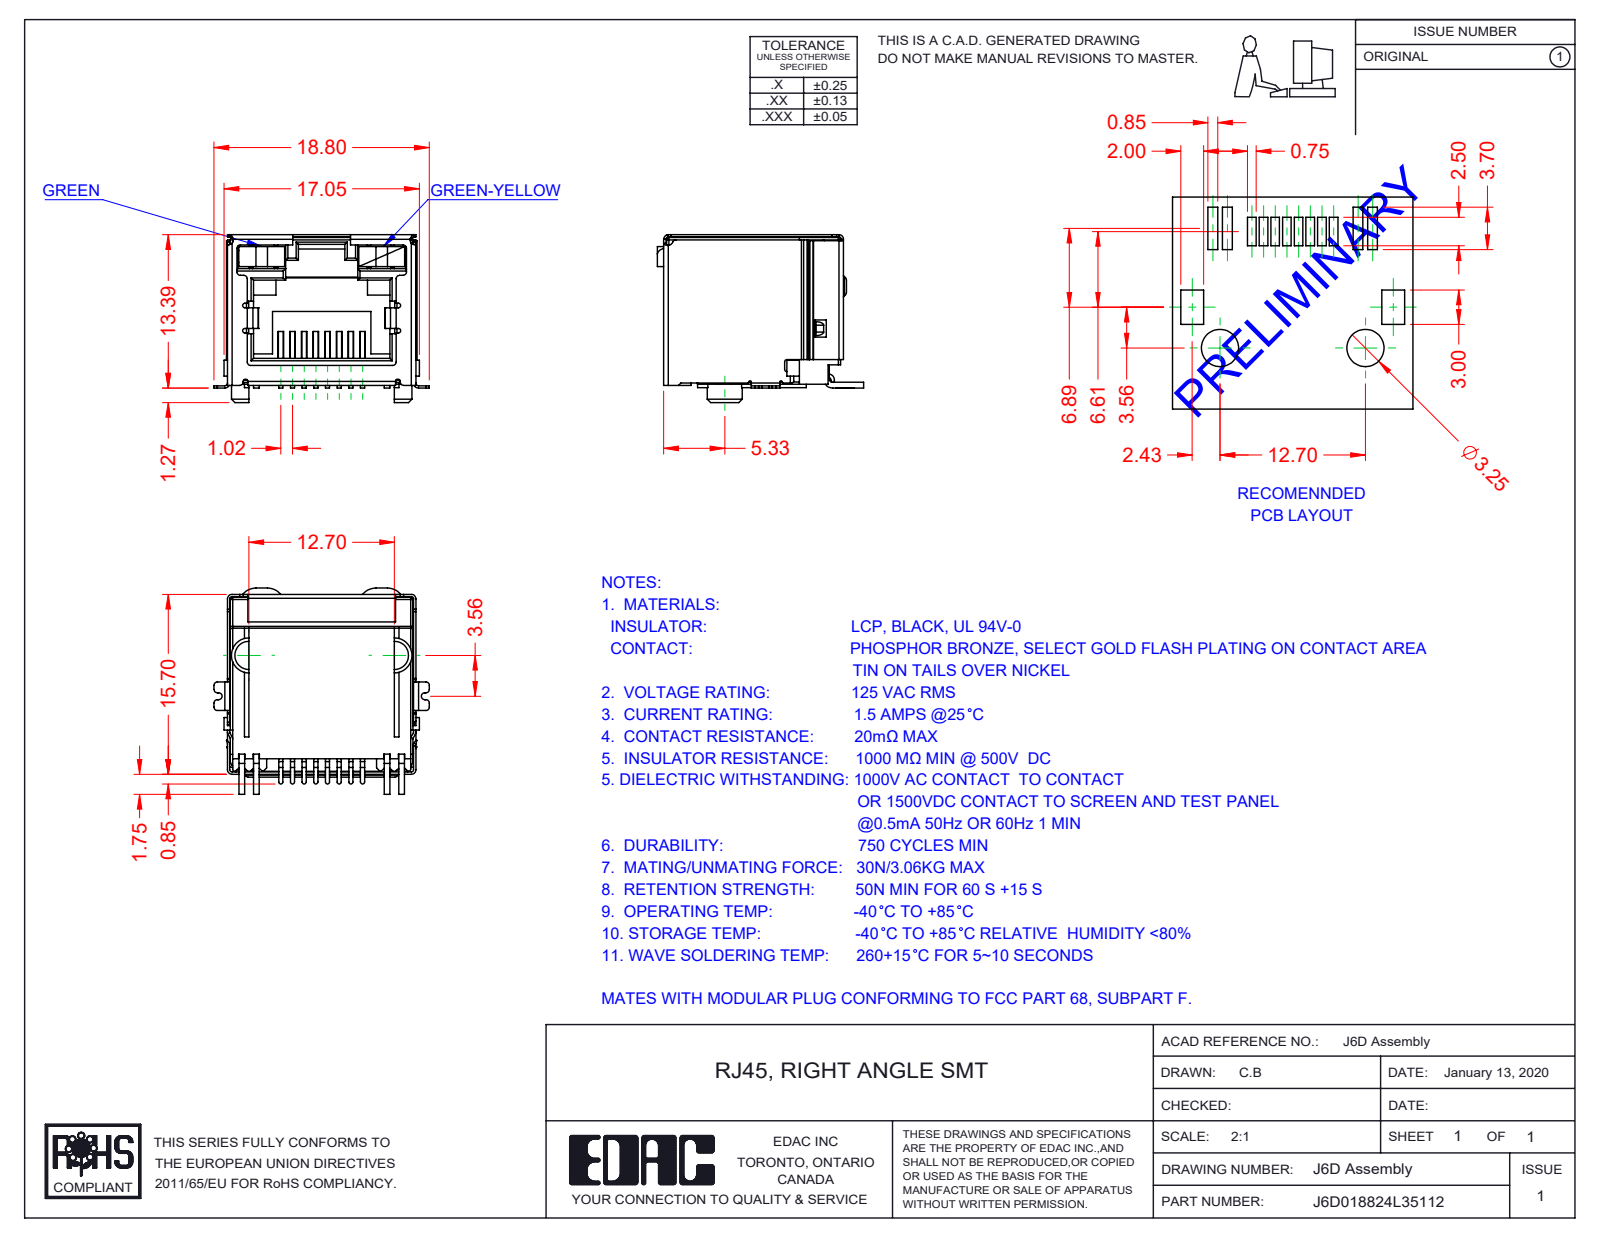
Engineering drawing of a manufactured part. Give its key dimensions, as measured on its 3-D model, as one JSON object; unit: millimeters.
{"part_name": "6D Shield_LED - No EMI; 6D LED RH_5-Green-Yellow; 6D Insulator; 6D LED LH_3-Green (+2 more)", "step_written_by": "SolidWorks 2016 (CONFIG_CONTROL_DESIGN)", "units": "millimeters", "bodies": {"solids": 12, "faces": 896, "planar": 645, "cylindrical": 218, "other": 33}, "overall_size": [18.8, 18, 14.65], "volume_mm3": 1804, "surface_area_mm2": 4898, "partial_cylinders_radius": [[0.3, 39], [0.2, 37], [0.4, 16], [0.1, 12], [0.15, 8], [0.18, 8], [0.5, 6], [1.5, 5]], "face_to_face_distances": [16, 16.25, 16.2, 2.25, 1, 15.95, 16.05, 12.8, 0.45, 16.45]}
